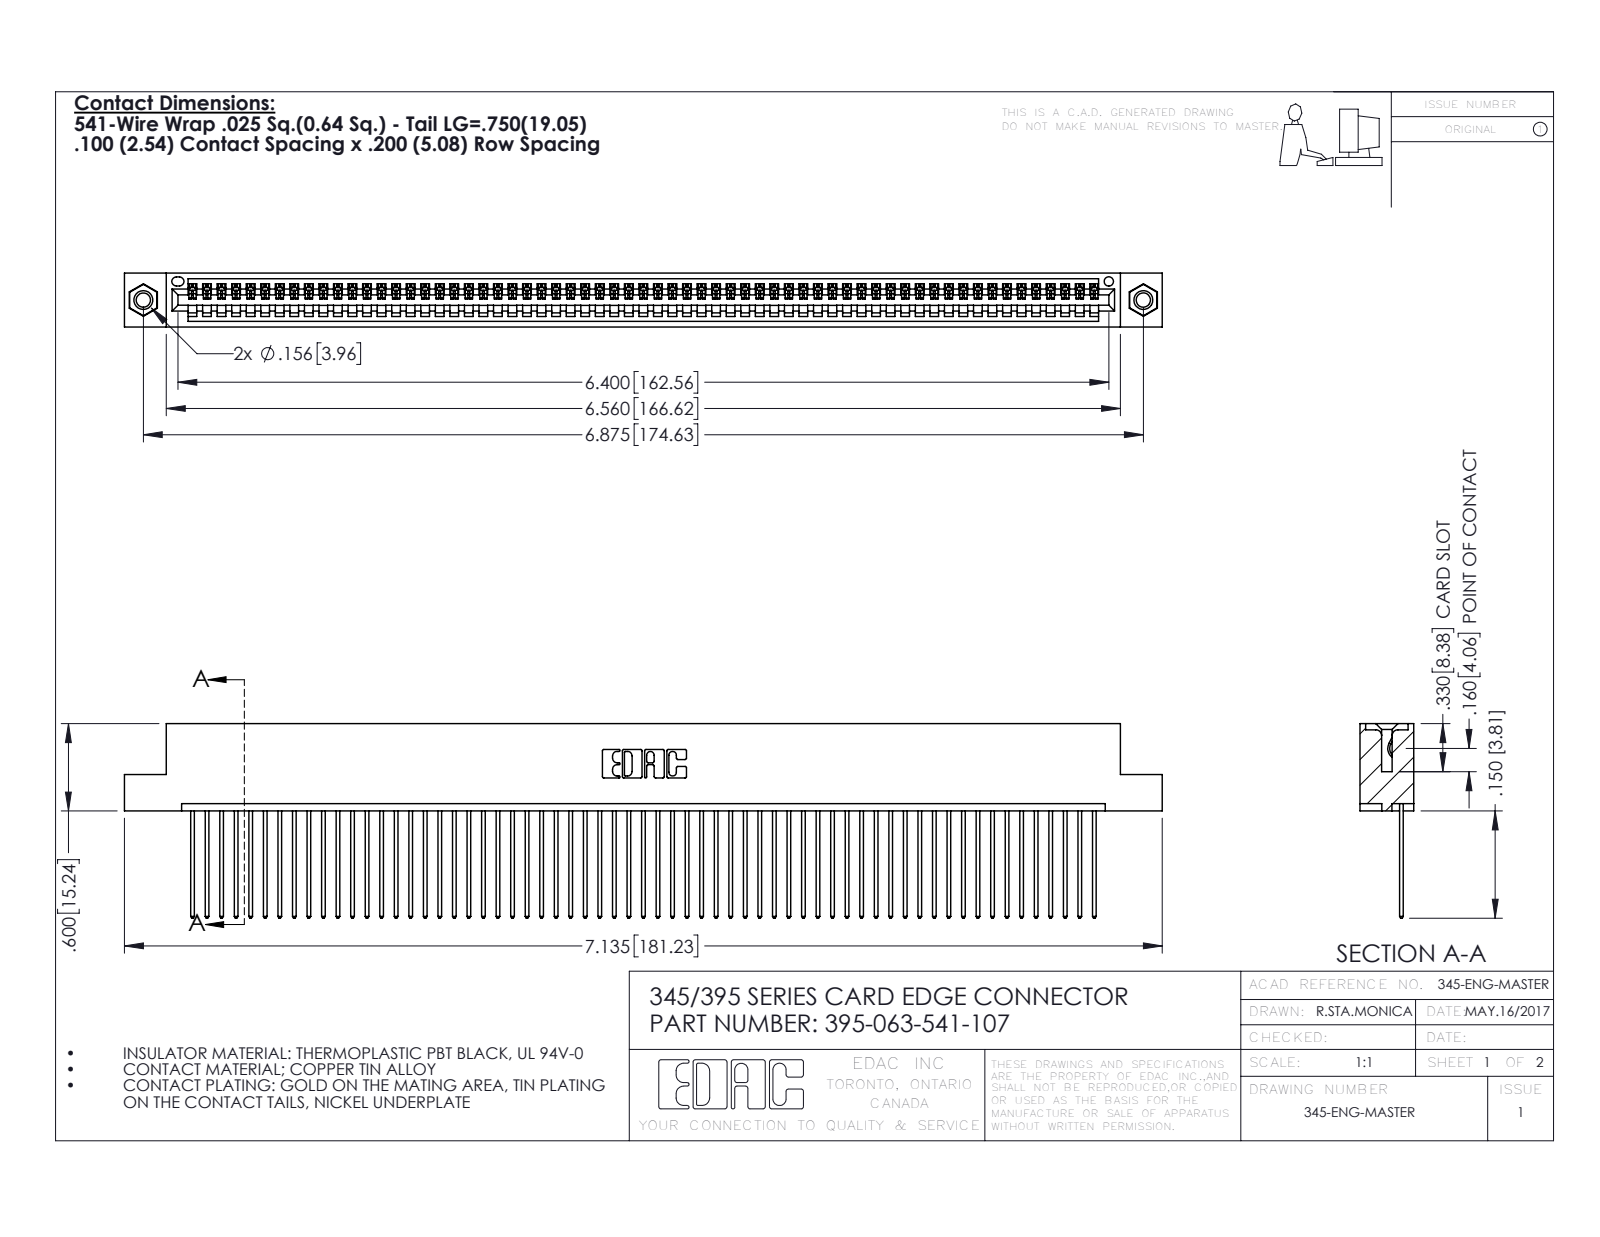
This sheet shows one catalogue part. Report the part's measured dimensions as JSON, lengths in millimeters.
{"part_name": "395-063-541-107; 345-250-001_345-250-005-103; 345-292-001_345-293-141; 345 Part_Flush Mounting Lugs - 0.156 Dia-TI", "step_written_by": "SolidWorks 2016 (CONFIG_CONTROL_DESIGN)", "units": "millimeters", "bodies": {"solids": 66, "faces": 3840, "planar": 2632, "cylindrical": 1192, "other": 16}, "overall_size": [181.2, 34, 9.4], "volume_mm3": 17580, "surface_area_mm2": 24900, "round_holes": [[2.5, 2], [3.2, 2], [4, 2], [1.6, 1]], "round_bosses_or_shafts": [[3.9, 2]], "partial_cylinders_radius": [[0.2, 126], [0.3, 126], [0.3, 22], [0.2, 6], [0.8, 6], [0.7, 3], [0.8, 2], [1, 2]], "face_to_face_distances": [1.8, 7.6, 2.5, 6.9, 0.6, 9.4, 5.1, 5.7, 3.8, 1.8], "hole_center_spacings": [6.9, 168.6, 174.6]}
